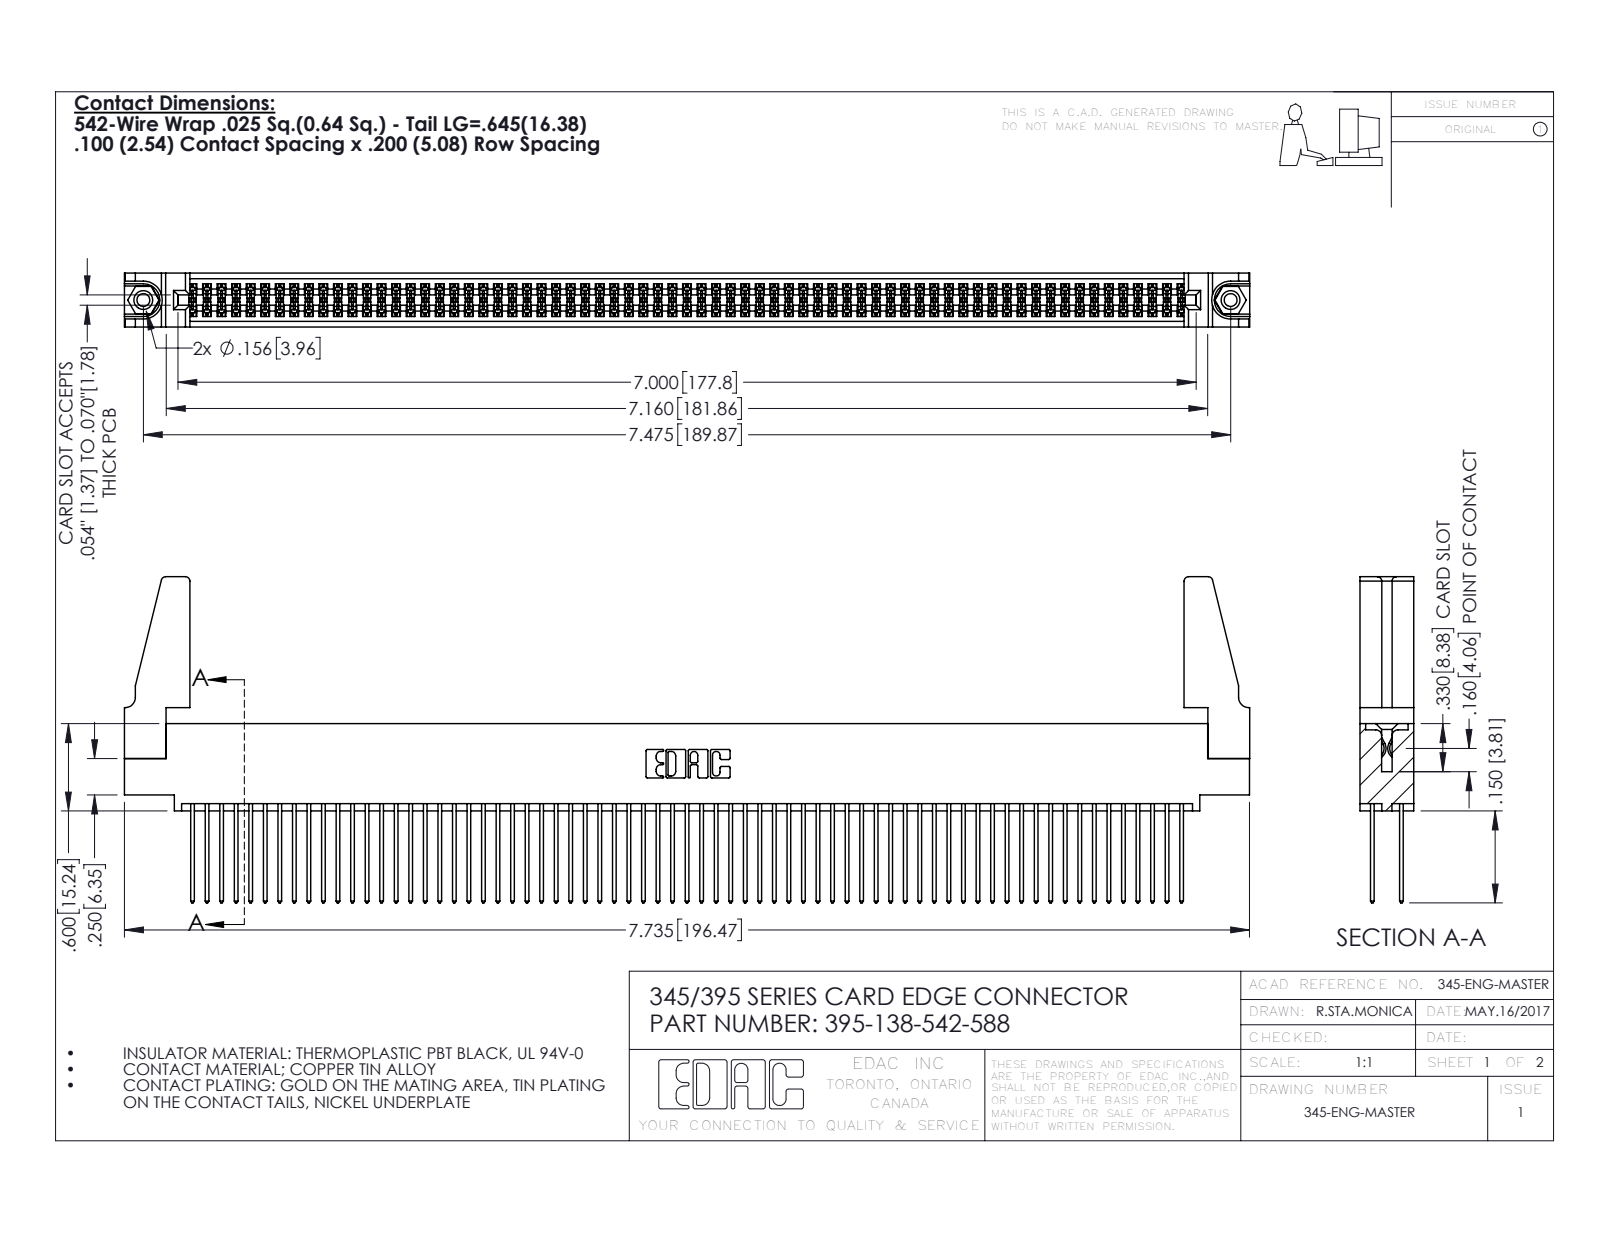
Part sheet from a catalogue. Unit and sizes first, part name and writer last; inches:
Units: inches
Overall size (bounding box): 7.736 × 2.242 × 0.37
Round holes (diameter × count): ⌀0.089 ×2, ⌀0.125 ×2, ⌀0.156 ×2, ⌀0.064 ×1
Round bosses / shafts (diameter × count): ⌀0.155 ×2
Partial cylindrical surfaces — rounded edges, fillets, slot ends (radius × count): R0.006 ×207, R0.01 ×138, R0.01 ×22, R0.03 ×8, R0.007 ×6, R0.031 ×6, R0.026 ×3, R0.014 ×2
Main face-to-face distances: 0.072, 0.298, 0.098, 0.272, 0.025, 0.2, 0.37, 0.225, 0.175, 0.149
Hole centre spacings: 0.27, 7.239, 7.475
Volume: 1.413 in³ · Surface area: 56.07 in²
Bodies: 143 solids, 7154 faces (4710 planar, 2428 cylindrical, 16 other)
Part name (STEP PRODUCT): 345 Part_0.110 Offset - 0.156 Dia-TH; 345-250-001_345-250-001-102; 345-220-078_345-220-088; 345-292-001_345-293-142 (+1 more)
STEP written by: SolidWorks 2016 (CONFIG_CONTROL_DESIGN)
